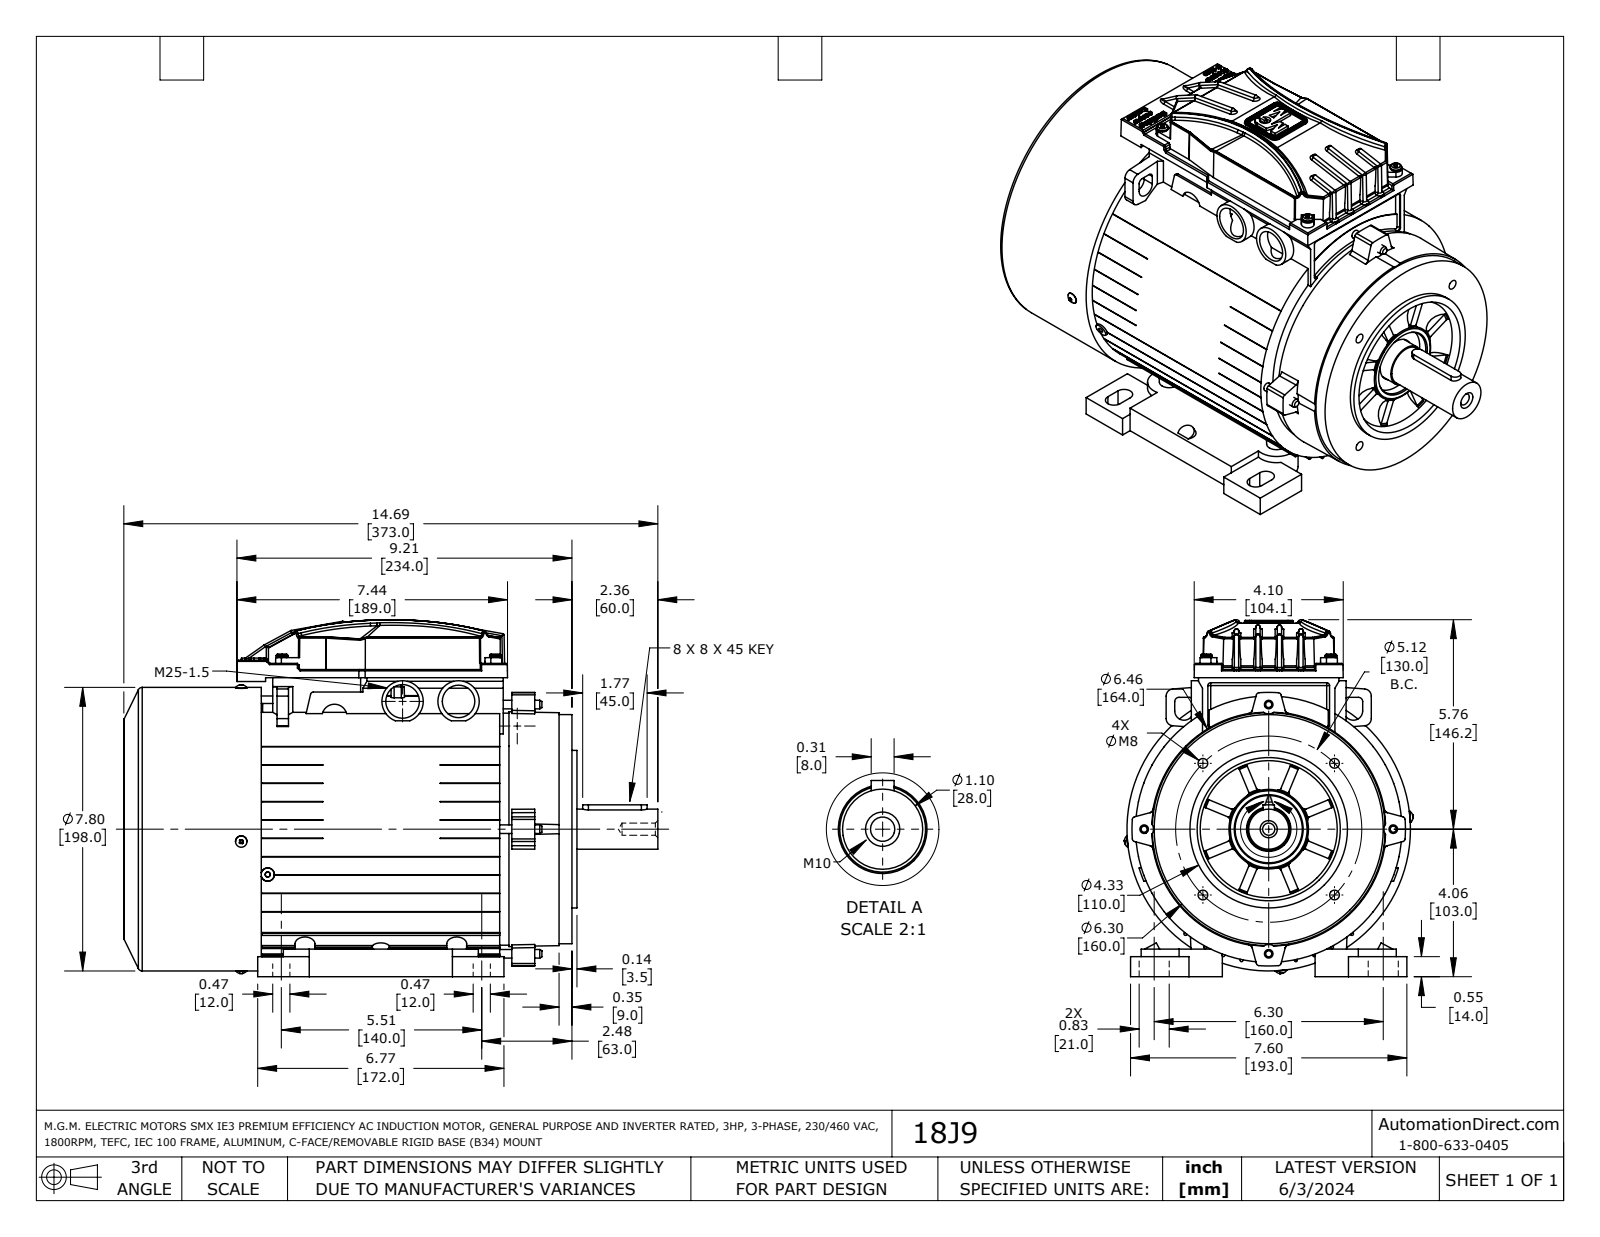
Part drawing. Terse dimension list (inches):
name: 18J9
written by: SolidWorks 2021 (AUTOMOTIVE_DESIGN)
unit: in
bodies: 15 solids, 3980 faces (1738 planar, 1252 cylindrical, 990 other)
size: 14.685 × 9.813 × 7.938
volume: 523.3 in³; area: 1 023 in²
holes: 7× ⌀0.13, 5× ⌀0.098, 5× ⌀0.335, 4× ⌀0.15, 4× ⌀0.157, 4× ⌀0.177, 4× ⌀0.197, 4× ⌀0.256, 4× ⌀0.268, 4× ⌀0.531, 2× ⌀0.118, 1× ⌀0.315
bosses: 12× ⌀0.315, 6× ⌀0.138, 4× ⌀0.522, 4× ⌀0.236, 4× ⌀0.079, 3× ⌀0.276, 2× ⌀1.138, 1× ⌀7.795
rounds: 540× R0.039, 56× R0.008, 48× R0.016, 47× R0.059, 30× R0.079, 24× R0.004, 20× R0.031, 16× R0.02
face distances: 8.74, 1.732, 10.492, 1.752, 10.472, 12.224, 1.987, 0.255, 8.485, 10.237
hole spacings: 2.426, 2.466, 4.886, 5.539, 5.594, 3.425, 0.059, 2.559
